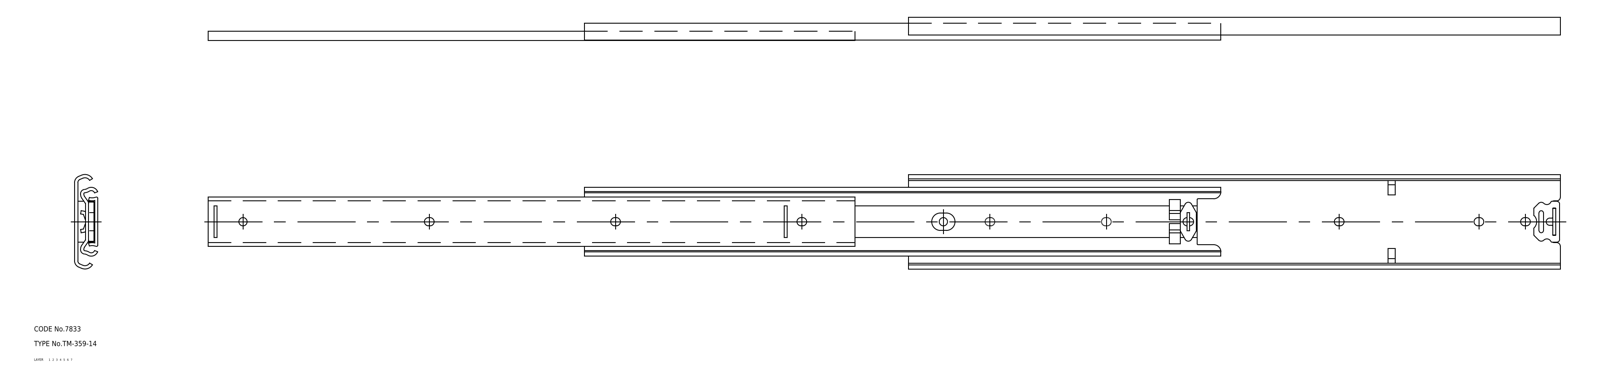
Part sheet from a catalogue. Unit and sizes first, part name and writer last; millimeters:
Units: millimetres
Overall size (bounding box): 737.6 × 51.5 × 12.8
Round holes (diameter × count): ⌀4.5 ×3
Partial cylindrical surfaces — rounded edges, fillets, slot ends (radius × count): R2.25 ×16, R2 ×11, R4.75 ×6, R0.45 ×4, R0.5 ×4, R0.6 ×4, R0.3 ×2, R0.77 ×2
Main face-to-face distances: 1.8, 5.91, 12.7, 10.9, 9.3, 11.1, 1.6, 4.11, 5.19, 6.79
Hole centre spacings: 170.7, 211.3, 382
Volume: 93 507 mm³ · Surface area: 109 074 mm²
Bodies: 3 solids, 233 faces (128 planar, 105 cylindrical, 0 other)
Part name (STEP PRODUCT): member_A; TM_359_14; member_C; member_B
STEP written by: SolidWorks 2015 (AUTOMOTIVE_DESIGN)
